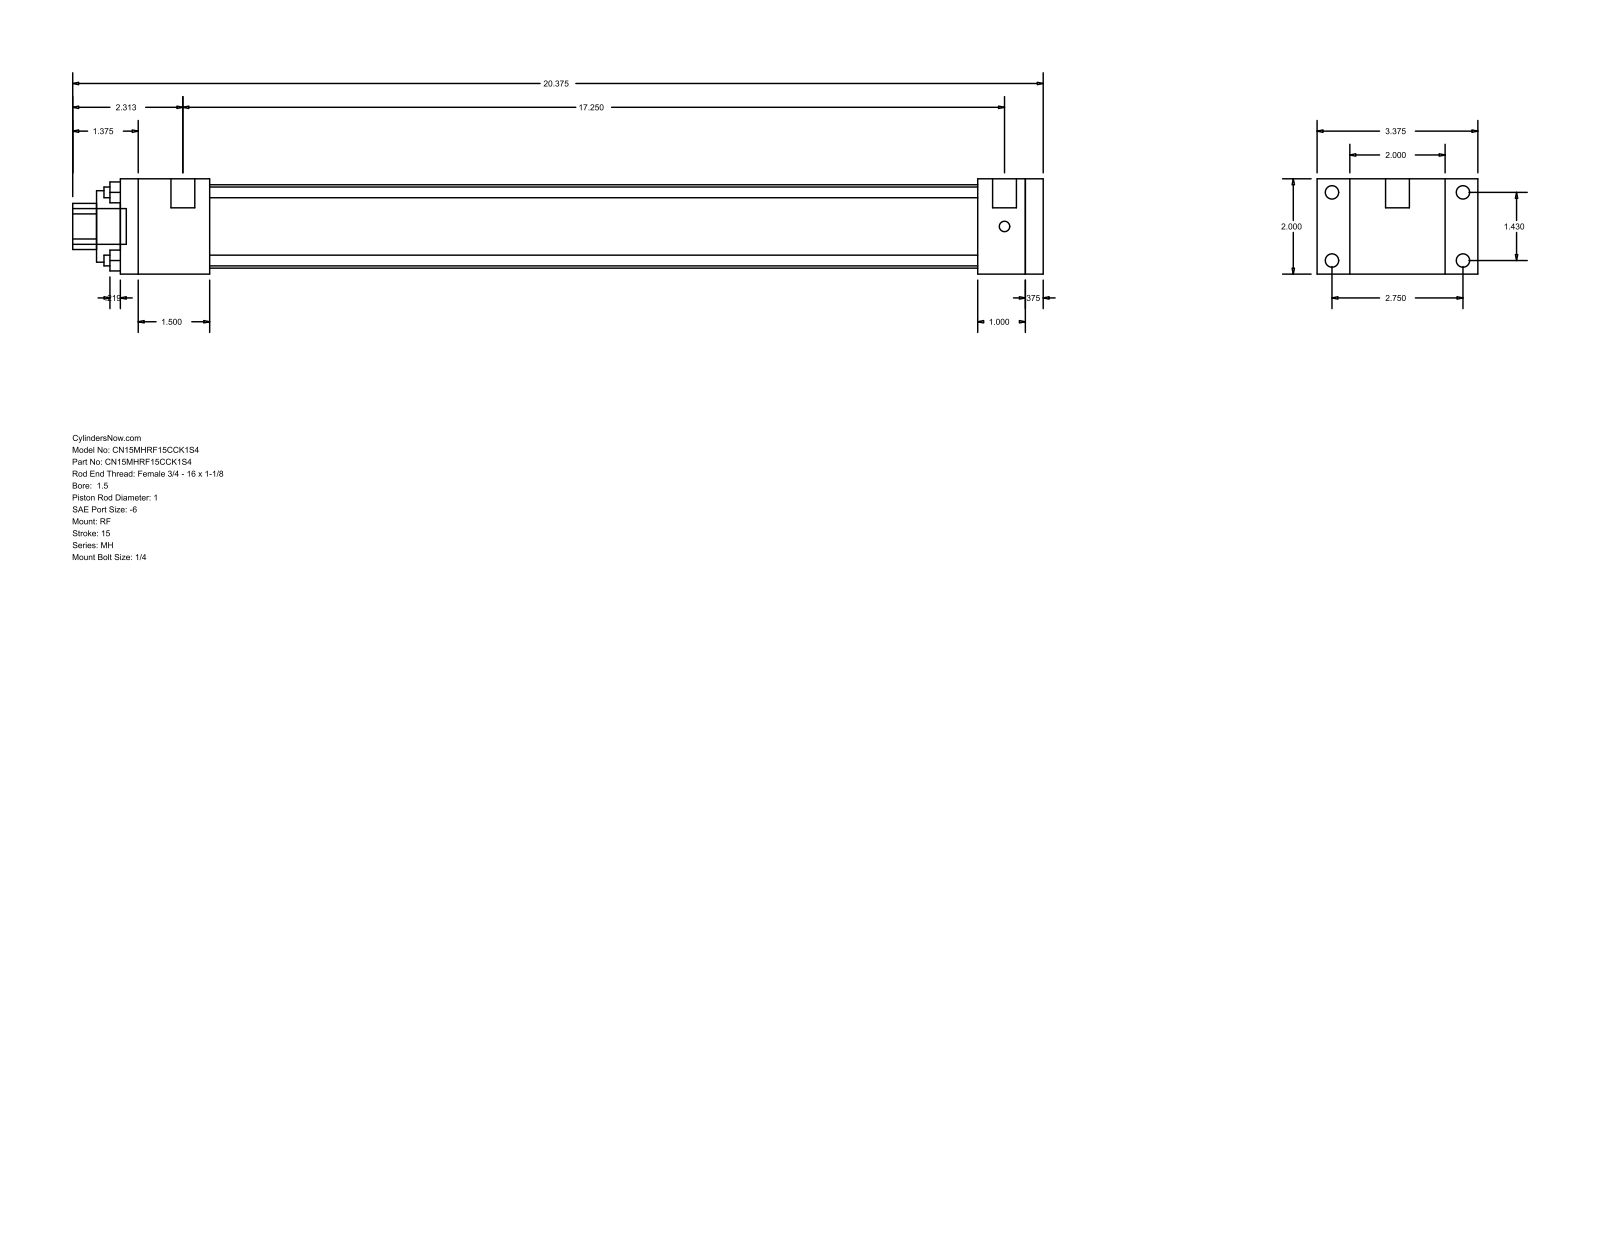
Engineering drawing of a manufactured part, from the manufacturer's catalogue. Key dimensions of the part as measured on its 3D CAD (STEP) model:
Part name (STEP PRODUCT): MH_RF__0150_1
STEP written by: GSSL Pune (CONFIG_CONTROL_DESIGN)
Units: millimetres
Bodies: 0 solids, 92 faces (64 planar, 28 cylindrical, 0 other)
Overall size (bounding box): 517.52 × 85.72 × 50.8
Round holes (diameter × count): ⌀5.71 ×4, ⌀25.4 ×1, ⌀38.1 ×1, ⌀44.45 ×1
Round bosses / shafts (diameter × count): ⌀7.14 ×4, ⌀5.56 ×4, ⌀12.7 ×2, ⌀19.05 ×1
Partial cylindrical surfaces — rounded edges, fillets, slot ends (radius × count): R12.29 ×1
Main face-to-face distances: 50.8, 9.52, 482.6, 25.4, 492.12, 17.46, 68.26, 457.2, 34.92, 47.63
Hole centre spacings: 25.68, 36.32, 51.36
